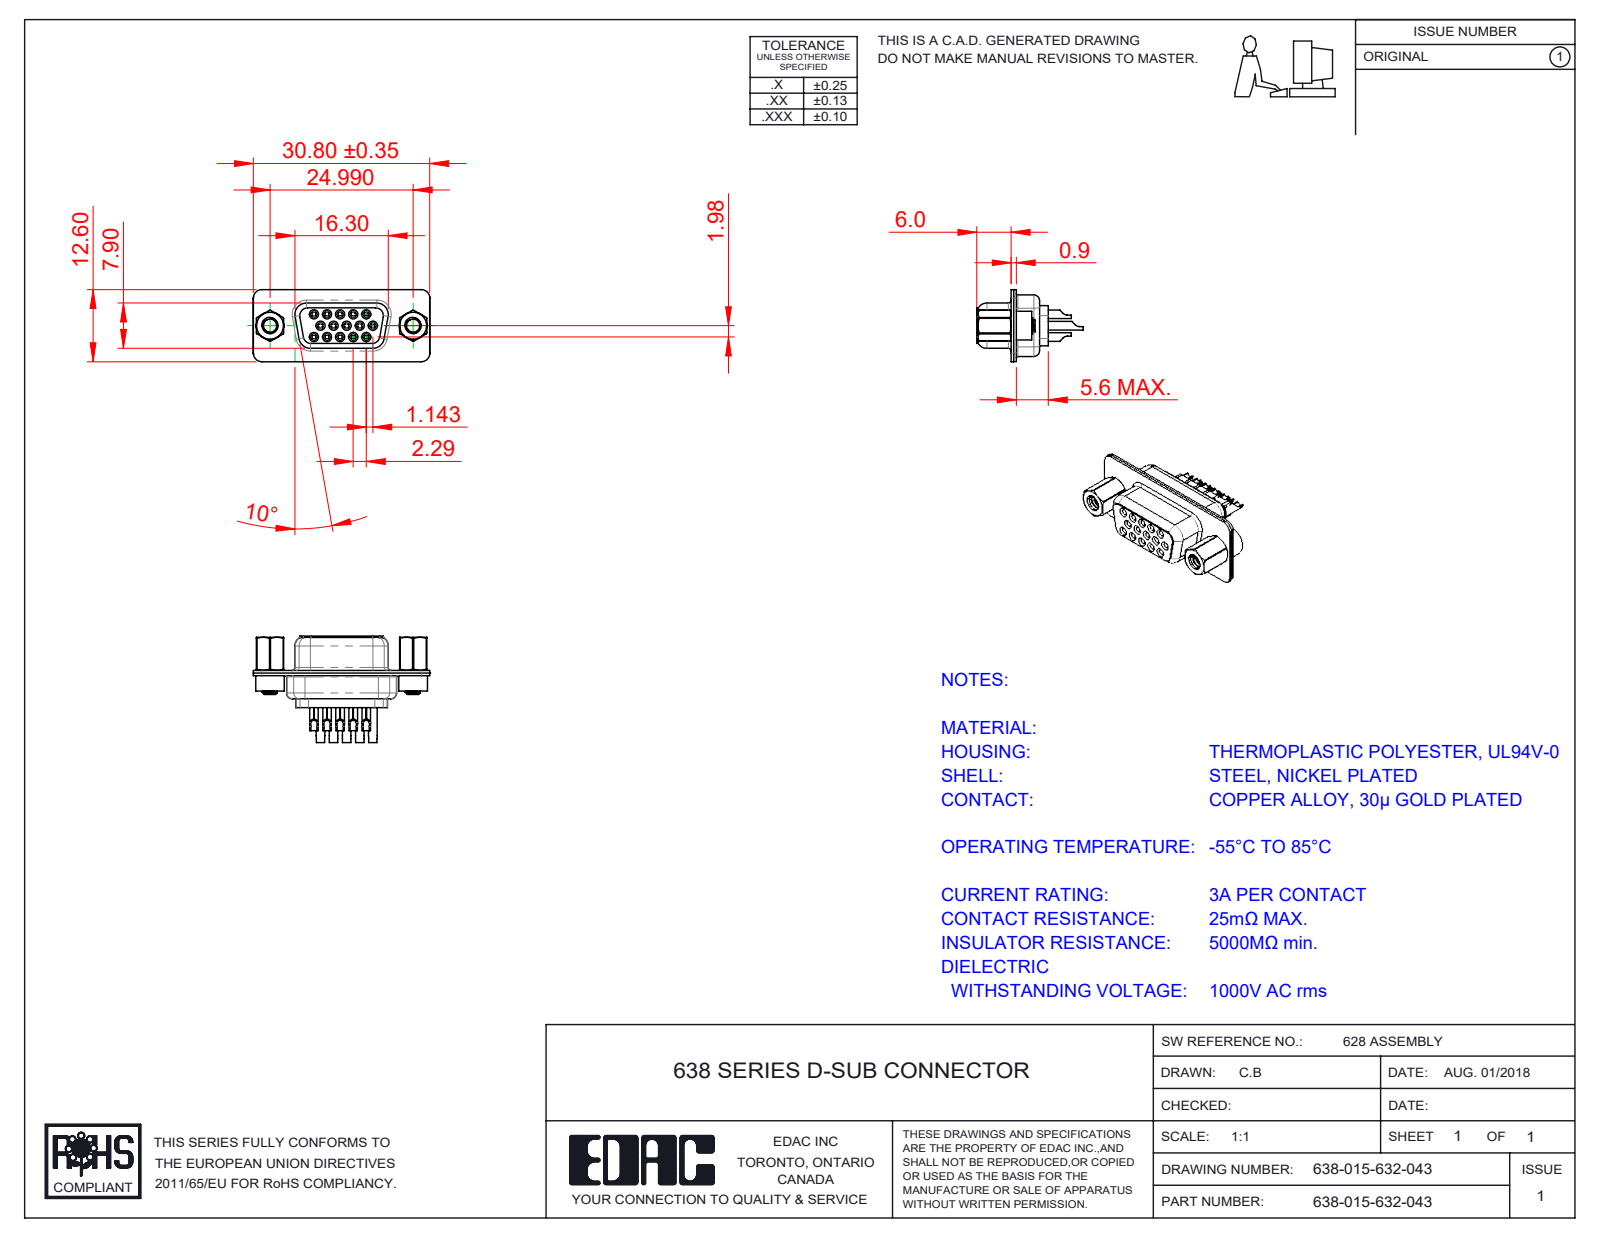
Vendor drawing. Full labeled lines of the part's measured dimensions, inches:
Part name (STEP PRODUCT): 638 4-40 Hex Standoff; 638 Shell Rear_15 Contacts; 638 Contact Row 1_32; 638 Contact Row 3_32 (+5 more)
STEP written by: SolidWorks 2020 (CONFIG_CONTROL_DESIGN)
Units: inches
Bodies: 22 solids, 1740 faces (404 planar, 584 cylindrical, 752 other)
Overall size (bounding box): 1.213 × 0.732 × 0.496
Volume: 0.111 in³ · Surface area: 9.833 in²
Round holes (diameter × count): ⌀0.031 ×15, ⌀0.039 ×15, ⌀0.043 ×15, ⌀0.063 ×15, ⌀0.067 ×15, ⌀0.071 ×15, ⌀0.079 ×2, ⌀0.089 ×2, ⌀0.09 ×2, ⌀0.157 ×2, ⌀0.159 ×2, ⌀0.191 ×2
Round bosses / shafts (diameter × count): ⌀0.079 ×15, ⌀0.059 ×15, ⌀0.047 ×15, ⌀0.197 ×2, ⌀0.195 ×2, ⌀0.189 ×2, ⌀0.11 ×2
Partial cylindrical surfaces — rounded edges, fillets, slot ends (radius × count): R0.059 ×20, R0.079 ×12, R0.011 ×10, R0.061 ×8, R0.039 ×7, R0.053 ×5, R0.01 ×4, R0.02 ×4
Main face-to-face distances: 0.018, 0.035, 0.016, 0.056, 0.35, 0.26, 0.055, 0.09, 0.244, 0.033
Hole centre spacings: 0.156, 0.09, 0.18, 0.09, 0.238, 0.238, 0.27, 0.312
